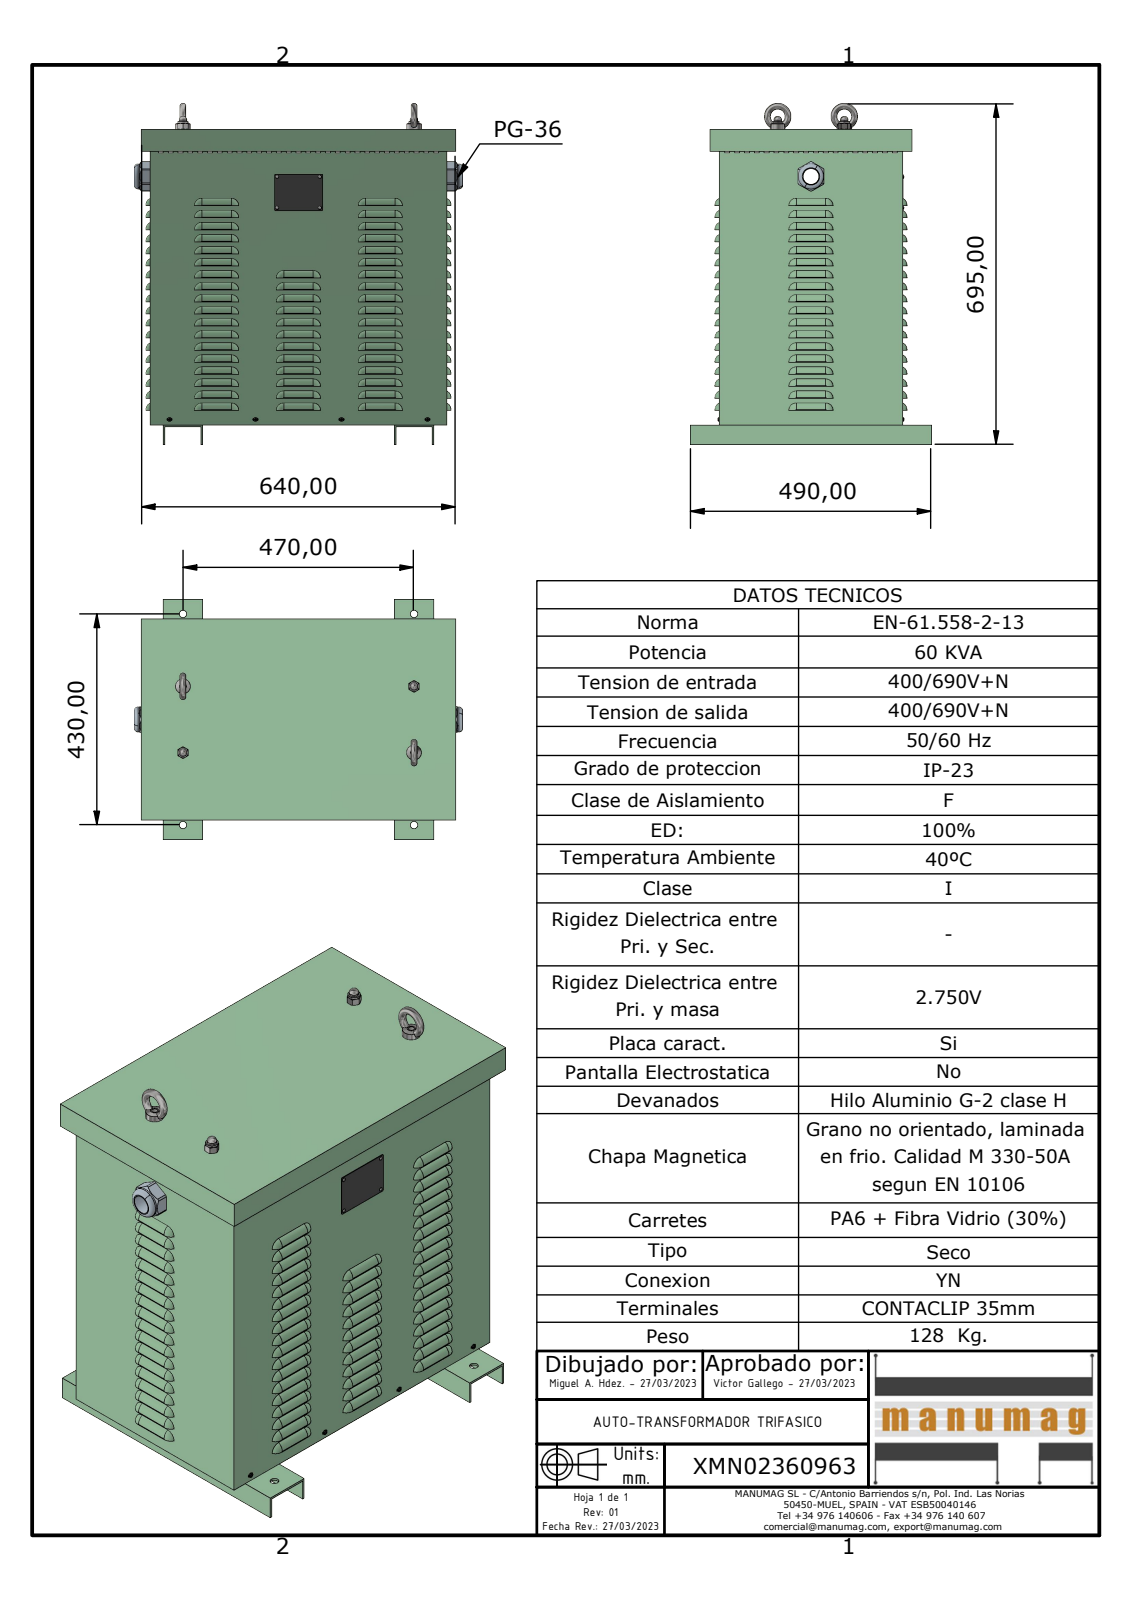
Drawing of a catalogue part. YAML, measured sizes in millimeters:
part_name: "XMN02360963; JE060 - JE075 CUERPO; JE060 - JE075 BASE; JE060 TAPA SUPERIOR (+7 more)"
step_written_by: "Autodesk Inventor 2023 (AUTOMOTIVE_DESIGN)"
units: millimeters
bodies: {solids: 24, faces: 2907, planar: 1145, cylindrical: 1024, other: 738}
overall_size: [695, 668.2, 490]
volume: 4615000
surface_area: 4047000
round_holes:
  - {diameter: 11, count: 364}
  - {diameter: 15, count: 8}
  - {diameter: 4, count: 4}
  - {diameter: 5, count: 4}
  - {diameter: 10.11, count: 2}
  - {diameter: 11.84, count: 2}
  - {diameter: 32, count: 1}
  - {diameter: 48, count: 1}
round_bosses_or_shafts:
  - {diameter: 4, count: 4}
  - {diameter: 3.62, count: 4}
  - {diameter: 3.2, count: 4}
  - {diameter: 51.1, count: 2}
  - {diameter: 30, count: 2}
  - {diameter: 21, count: 2}
  - {diameter: 15.6, count: 2}
  - {diameter: 47.45, count: 1}
partial_cylinders:
  - {radius: 14, count: 132}
  - {radius: 7, count: 72}
  - {radius: 15, count: 72}
  - {radius: 3.88, count: 12}
  - {radius: 2.5, count: 8}
  - {radius: 7.5, count: 8}
  - {radius: 2, count: 4}
  - {radius: 30, count: 2}
face_to_face_distances: [2, 370, 600, 601, 368, 372, 602, 599, 598, 603]
hole_center_spacings: [30, 21.21, 132, 128.88, 147, 173.76, 279, 469.24]
